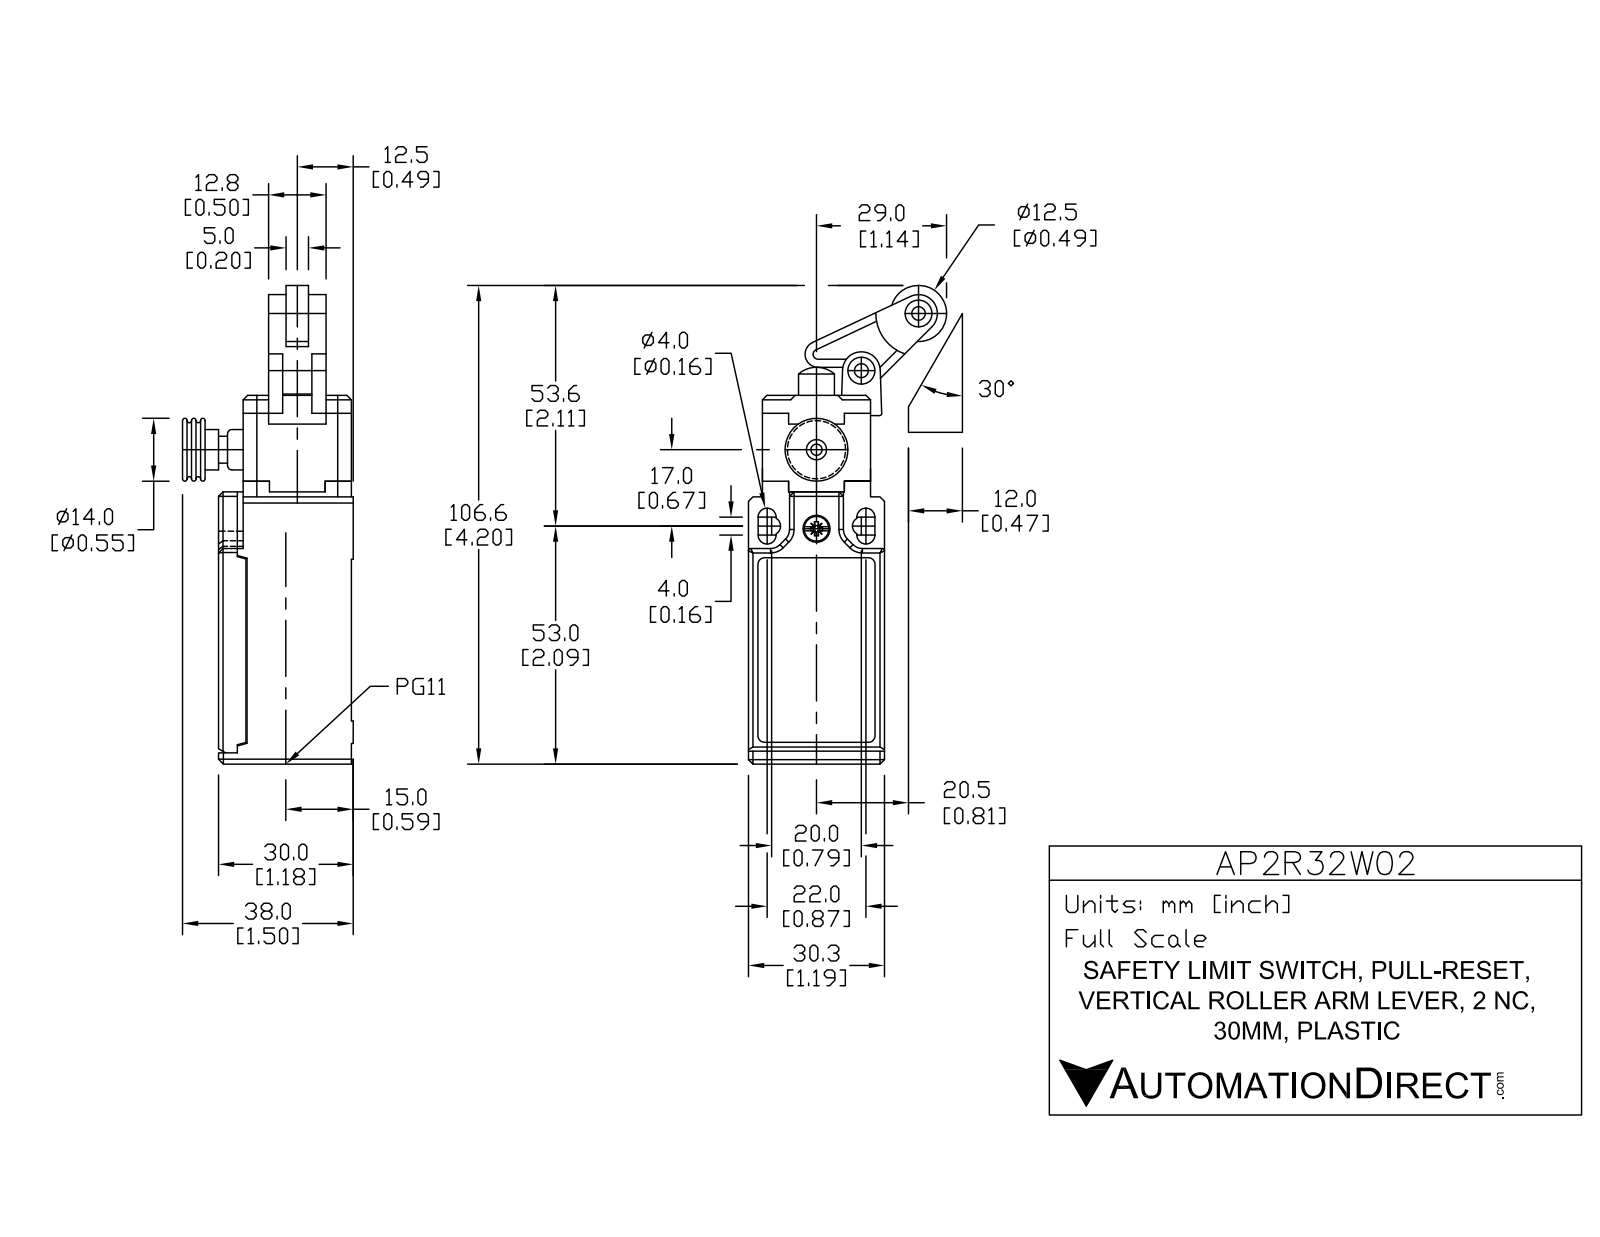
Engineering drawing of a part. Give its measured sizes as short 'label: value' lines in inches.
name: AP2R32W02
written by: SolidWorks 2017 (AUTOMOTIVE_DESIGN)
unit: in
bodies: 6 solids, 308 faces (161 planar, 102 cylindrical, 45 other)
size: 4.255 × 1.743 × 1.474
volume: 4.123 in³; area: 29.71 in²
holes: 1× ⌀0.319, 1× ⌀0.669, 1× ⌀0.748
bosses: 4× ⌀0.22, 3× ⌀0.217, 1× ⌀0.492, 1× ⌀0.386, 1× ⌀0.354, 1× ⌀0.315, 1× ⌀0.307, 1× ⌀0.276
rounds: 10× R0.039, 8× R0.118, 6× R0.079, 4× R0.02, 2× R0.157, 1× R0.043, 1× R0.114, 1× R0.165
face distances: 1.193, 1.165, 0.945, 0.124, 1.069, 0.236, 0.094, 0.594, 0.016, 0.22
hole spacings: 0.083
